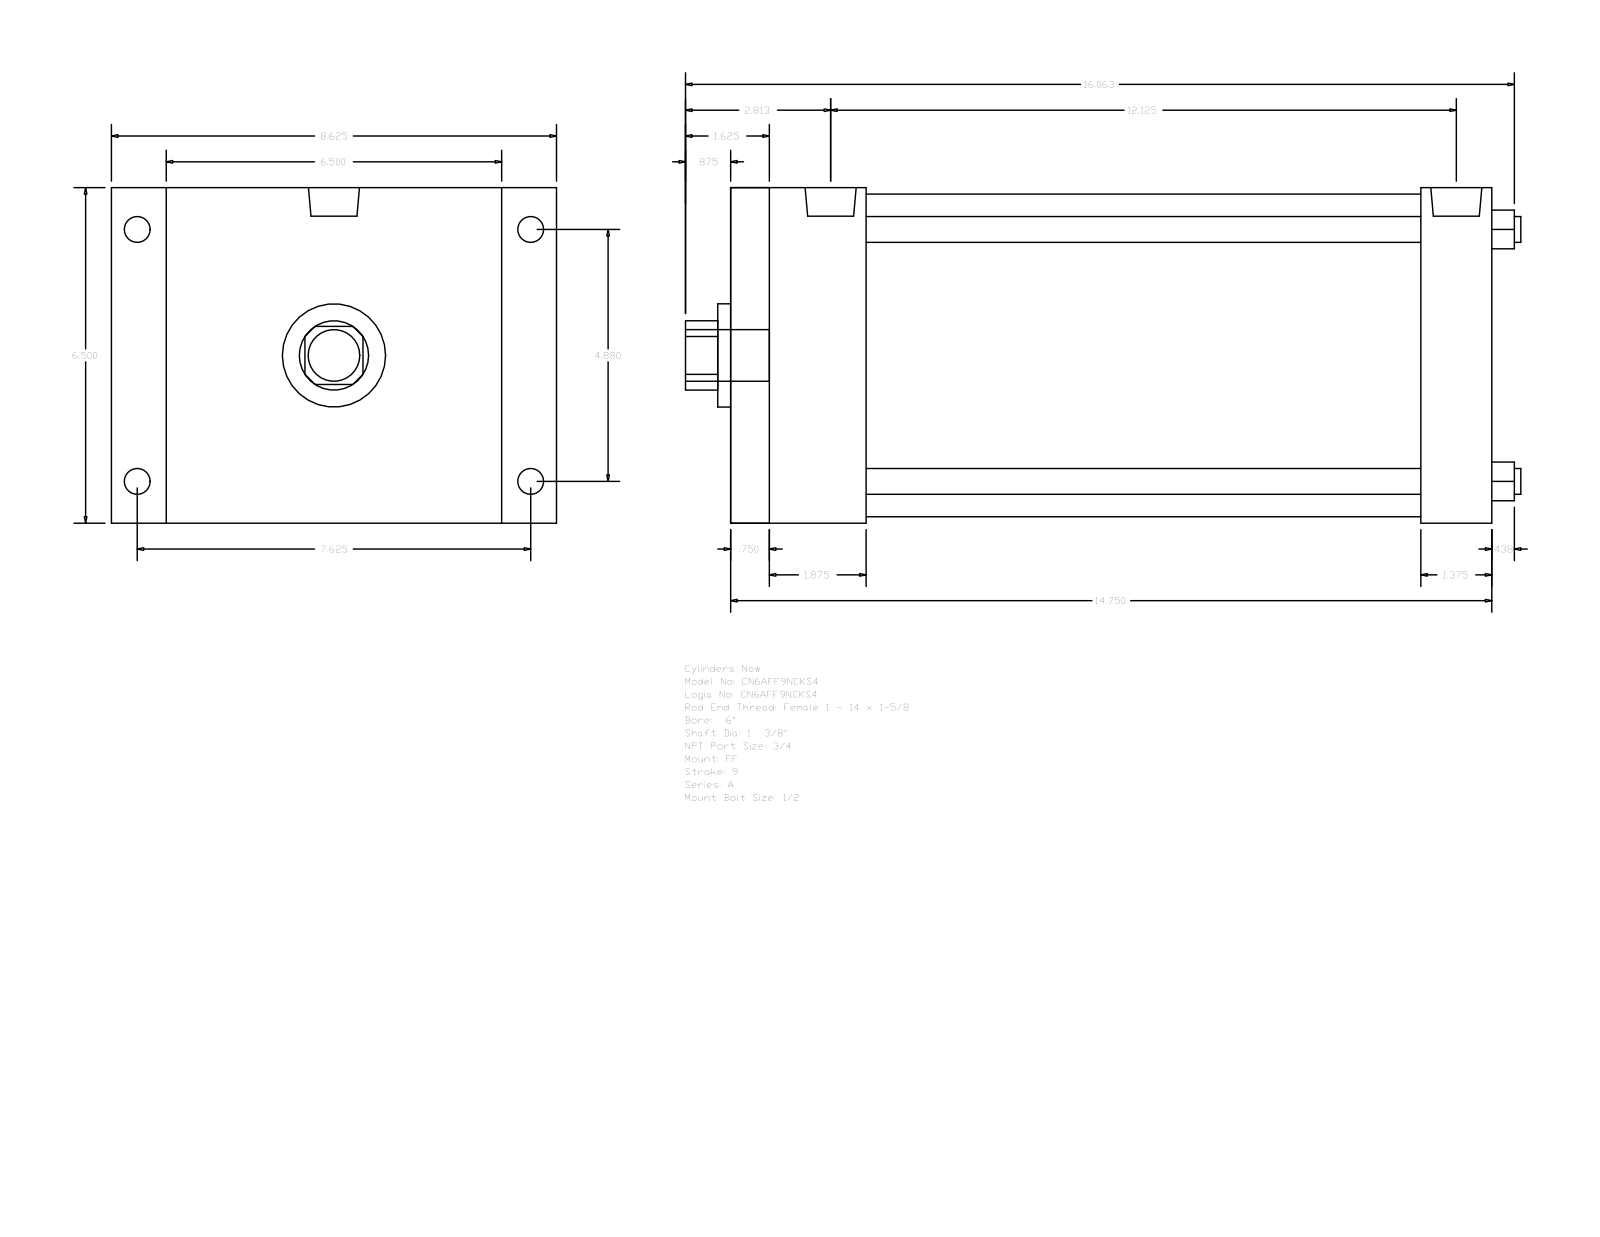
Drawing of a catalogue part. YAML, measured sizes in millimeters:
part_name: "A_FF__0600_1.375"
step_written_by: "GSSL Pune (CONFIG_CONTROL_DESIGN)"
units: millimeters
bodies: {solids: 0, faces: 92, planar: 64, cylindrical: 28, other: 0}
overall_size: [411.16, 219.07, 165.1]
round_holes:
  - {diameter: 12.7, count: 4}
  - {diameter: 34.92, count: 1}
  - {diameter: 50.8, count: 1}
  - {diameter: 158.75, count: 1}
round_bosses_or_shafts:
  - {diameter: 15.08, count: 4}
  - {diameter: 12.7, count: 4}
  - {diameter: 25.12, count: 2}
  - {diameter: 25.4, count: 1}
partial_cylinders:
  - {radius: 17.06, count: 1}
face_to_face_distances: [165.1, 374.65, 19.04, 355.61, 66.67, 47.63, 307.98, 339.72, 320.68, 273.05]
hole_center_spacings: [87.65, 123.96, 175.31]
